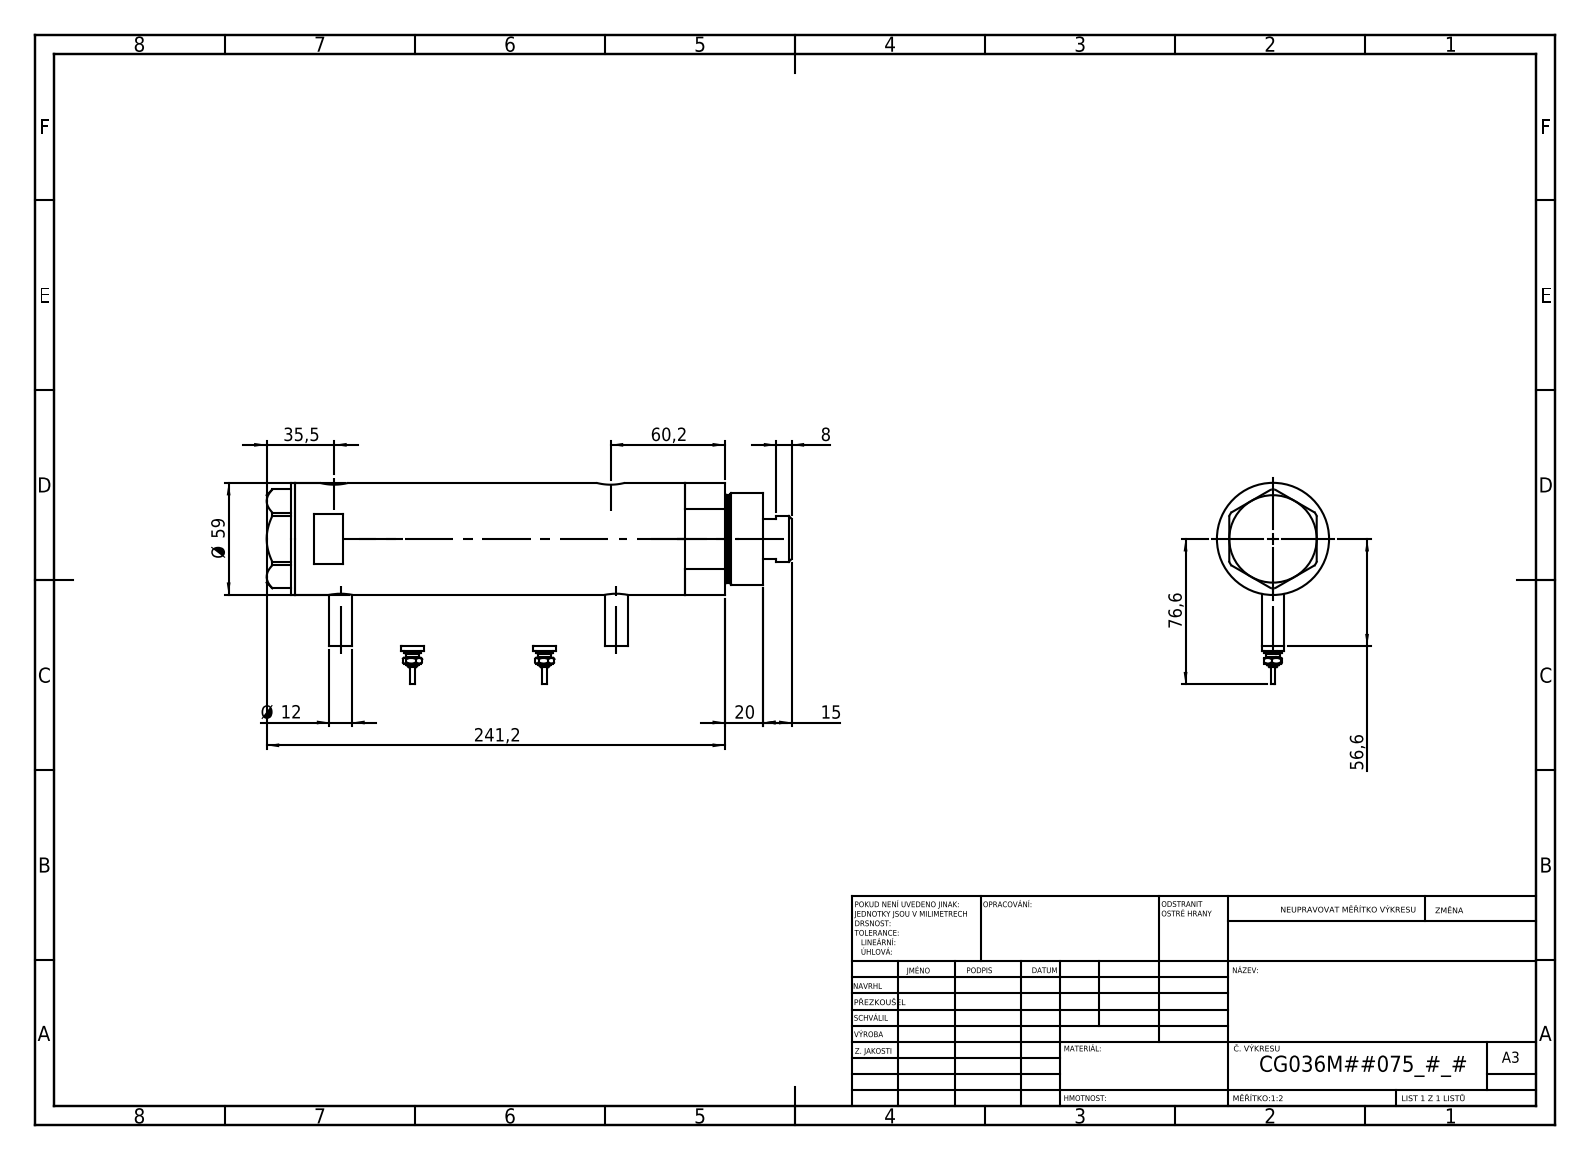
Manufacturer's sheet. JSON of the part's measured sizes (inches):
{"part_name": "V270CG_MIDDLE; Switch; V270CG_FRONT; V270CG_BACK (+1 more)", "step_written_by": "SolidWorks 2019 (CONFIG_CONTROL_DESIGN)", "units": "inches", "bodies": {"solids": 6, "faces": 212, "planar": 79, "cylindrical": 69, "other": 64}, "overall_size": [10.874, 4.177, 2.323], "volume_in3": 39.6, "surface_area_in2": 199.4, "round_holes": [[0.383, 2], [0.492, 2], [0.591, 2], [0.335, 1], [0.984, 1], [1.043, 1], [1.417, 1], [1.575, 1], [2.047, 1]], "round_bosses_or_shafts": [[0.472, 4], [0.354, 2], [0.276, 2], [0.177, 2], [0.098, 2], [2.323, 1], [1.89, 1], [1.811, 1]], "face_to_face_distances": [6.583, 0.925, 5.657, 0.591, 1.516, 7.173, 0.079, 10.283, 9.693, 8.768], "hole_center_spacings": [0.114, 0.138, 5.591, 5.705, 5.728, 5.843]}
